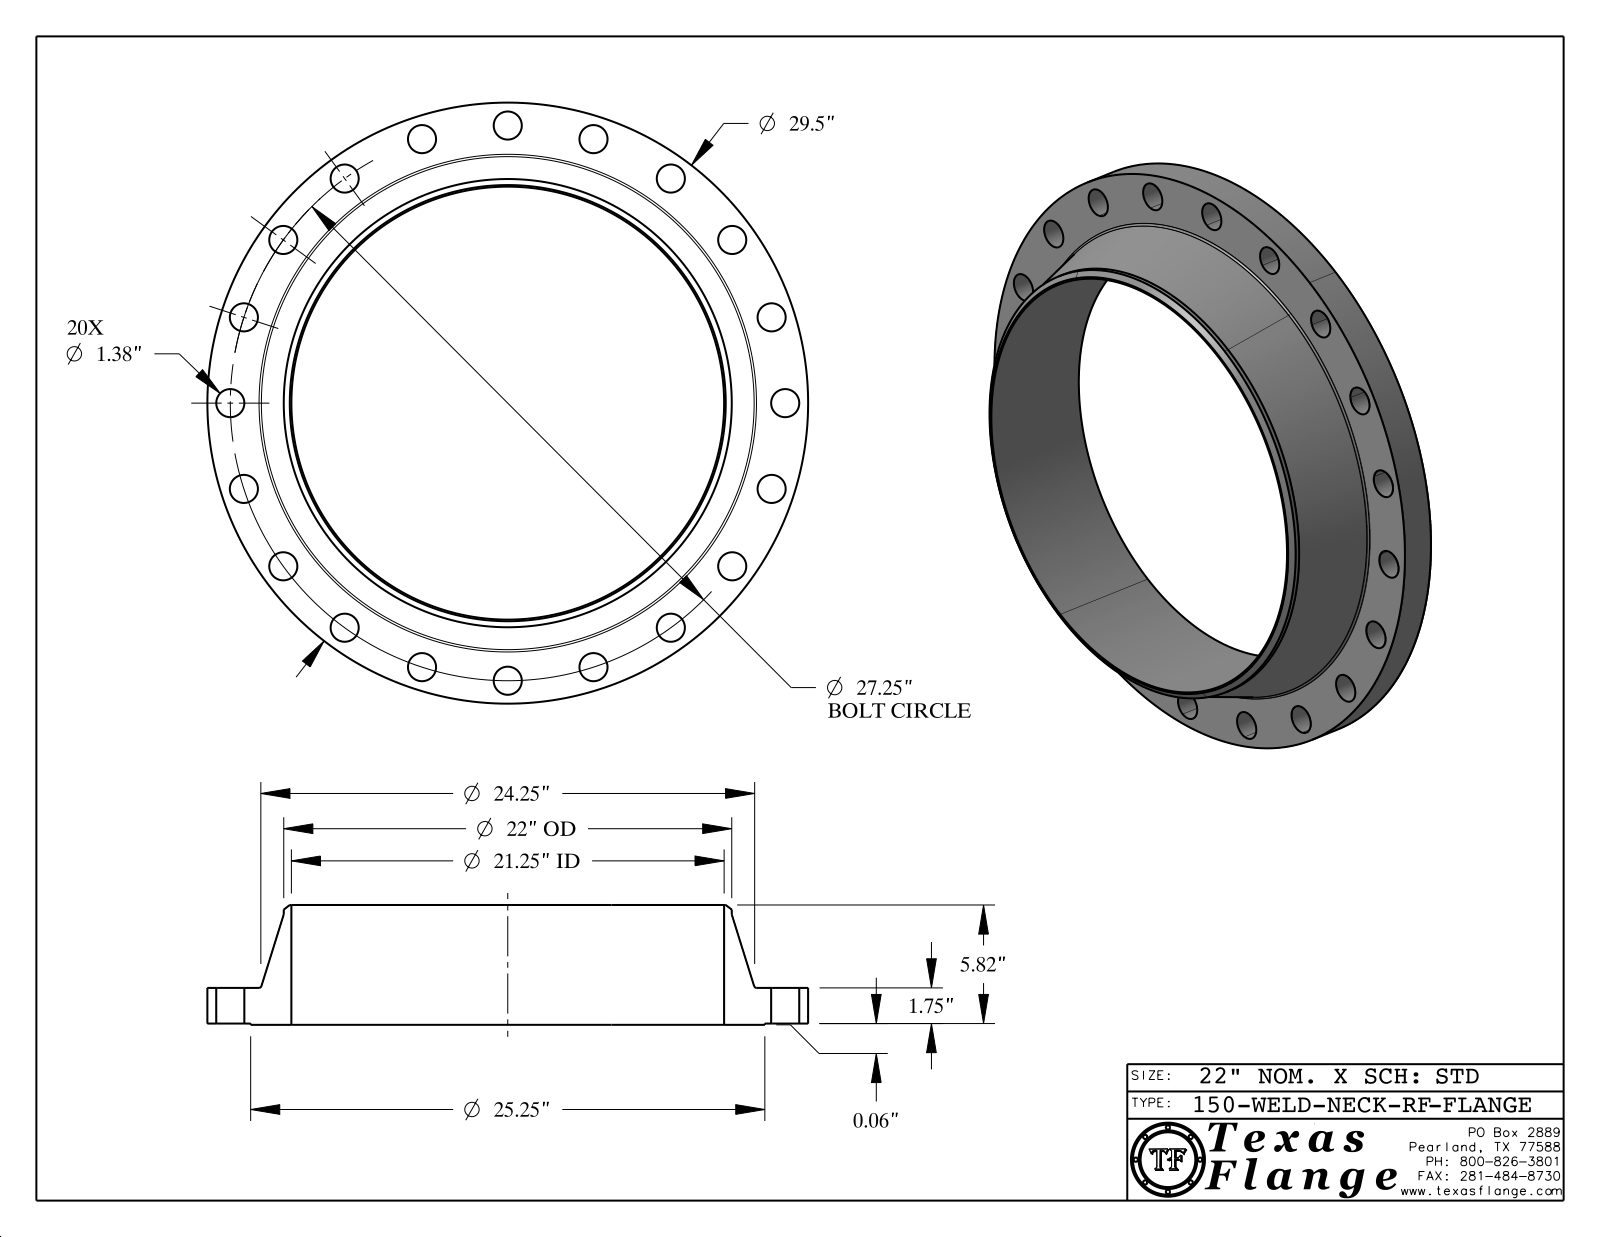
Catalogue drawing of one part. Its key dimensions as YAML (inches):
part_name: "150-WELD-NECK-RF"
step_written_by: "CATIA V5 STEP AP214 (AUTOMOTIVE_DESIGN)"
units: inches
bodies: {solids: 1, faces: 443, planar: 369, cylindrical: 68, other: 6}
overall_size: [29.5, 29.5, 5.883]
volume: 778.7
surface_area: 1522
round_holes:
  - {diameter: 1.38, count: 20}
  - {diameter: 0.495, count: 1}
  - {diameter: 21.25, count: 1}
round_bosses_or_shafts:
  - {diameter: 0.03, count: 8}
  - {diameter: 29.5, count: 1}
  - {diameter: 25.25, count: 1}
  - {diameter: 22, count: 1}
  - {diameter: 0.39, count: 1}
face_to_face_distances: [1.75, 0.063, 1.813, 5.883, 5.82, 4.07, 1.798, 1.735, 0.015, 4.085]
hole_center_spacings: [13.625, 19.269, 25.917, 8.421, 12.371, 4.263, 16.017, 22.046]
